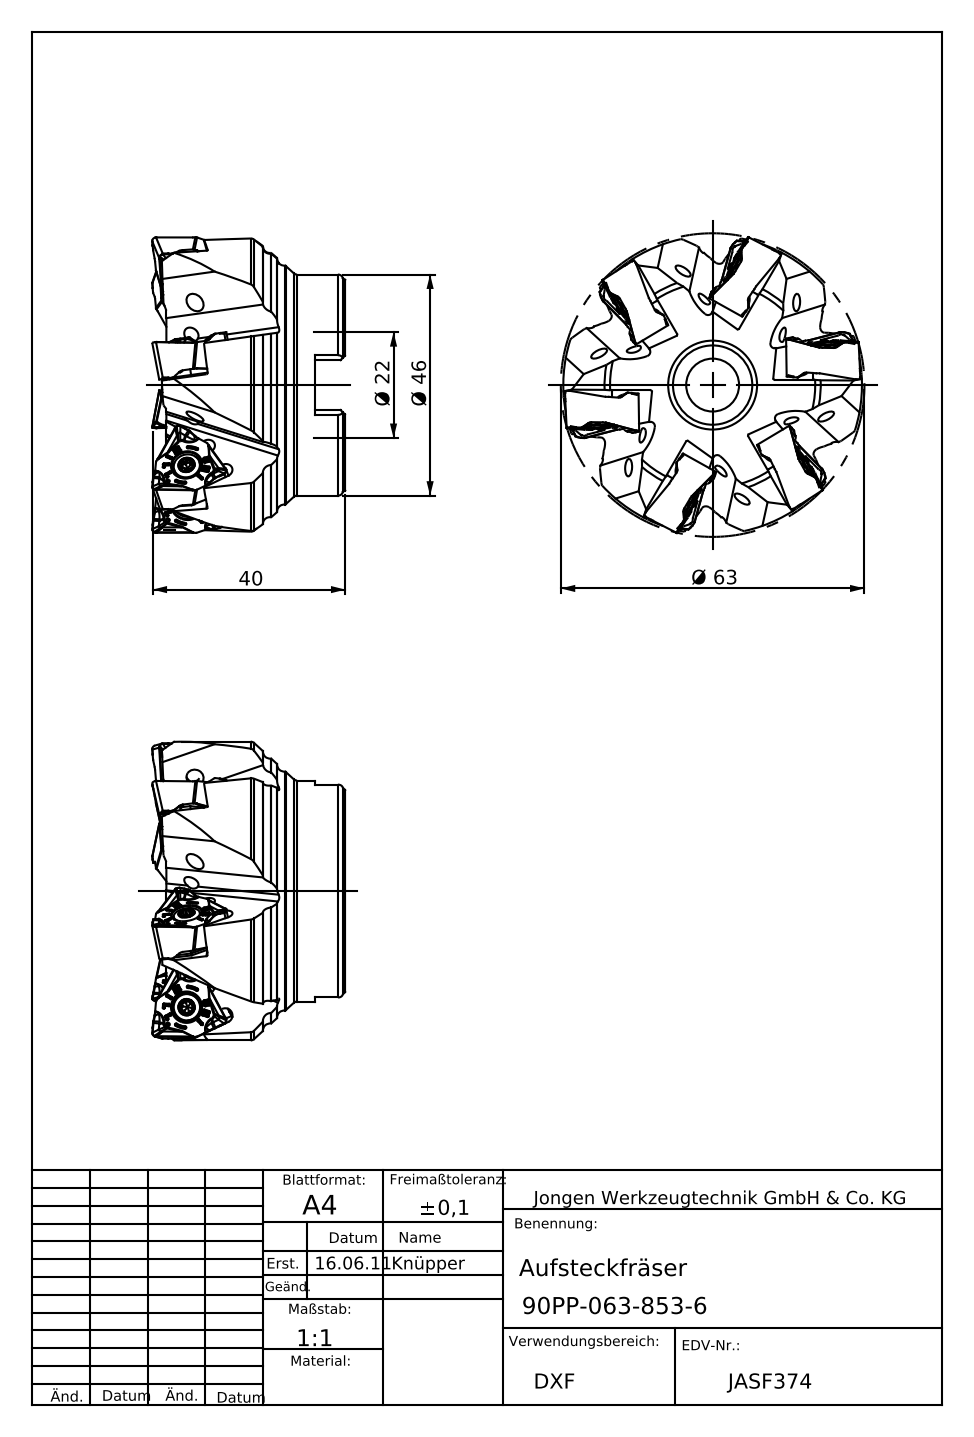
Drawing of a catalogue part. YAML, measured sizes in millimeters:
part_name: "90PP-63-853-6"
step_written_by: "SolidWorks 2010 (AUTOMOTIVE_DESIGN)"
units: millimeters
bodies: {solids: 1, faces: 368, planar: 108, cylindrical: 111, other: 149}
overall_size: [63.01, 63.01, 40]
volume: 74911
surface_area: 19019
round_holes:
  - {diameter: 3, count: 6}
  - {diameter: 11, count: 1}
  - {diameter: 16.5, count: 1}
  - {diameter: 22, count: 1}
  - {diameter: 22.15, count: 1}
  - {diameter: 22.3, count: 1}
round_bosses_or_shafts:
  - {diameter: 63, count: 1}
  - {diameter: 62.15, count: 1}
  - {diameter: 46, count: 1}
partial_cylinders:
  - {radius: 0.3, count: 42}
  - {radius: 1.5, count: 12}
face_to_face_distances: [37.25, 38.2, 0.95, 6.5, 6.35, 30.9, 31.85, 23.05, 16.7, 14.2]
